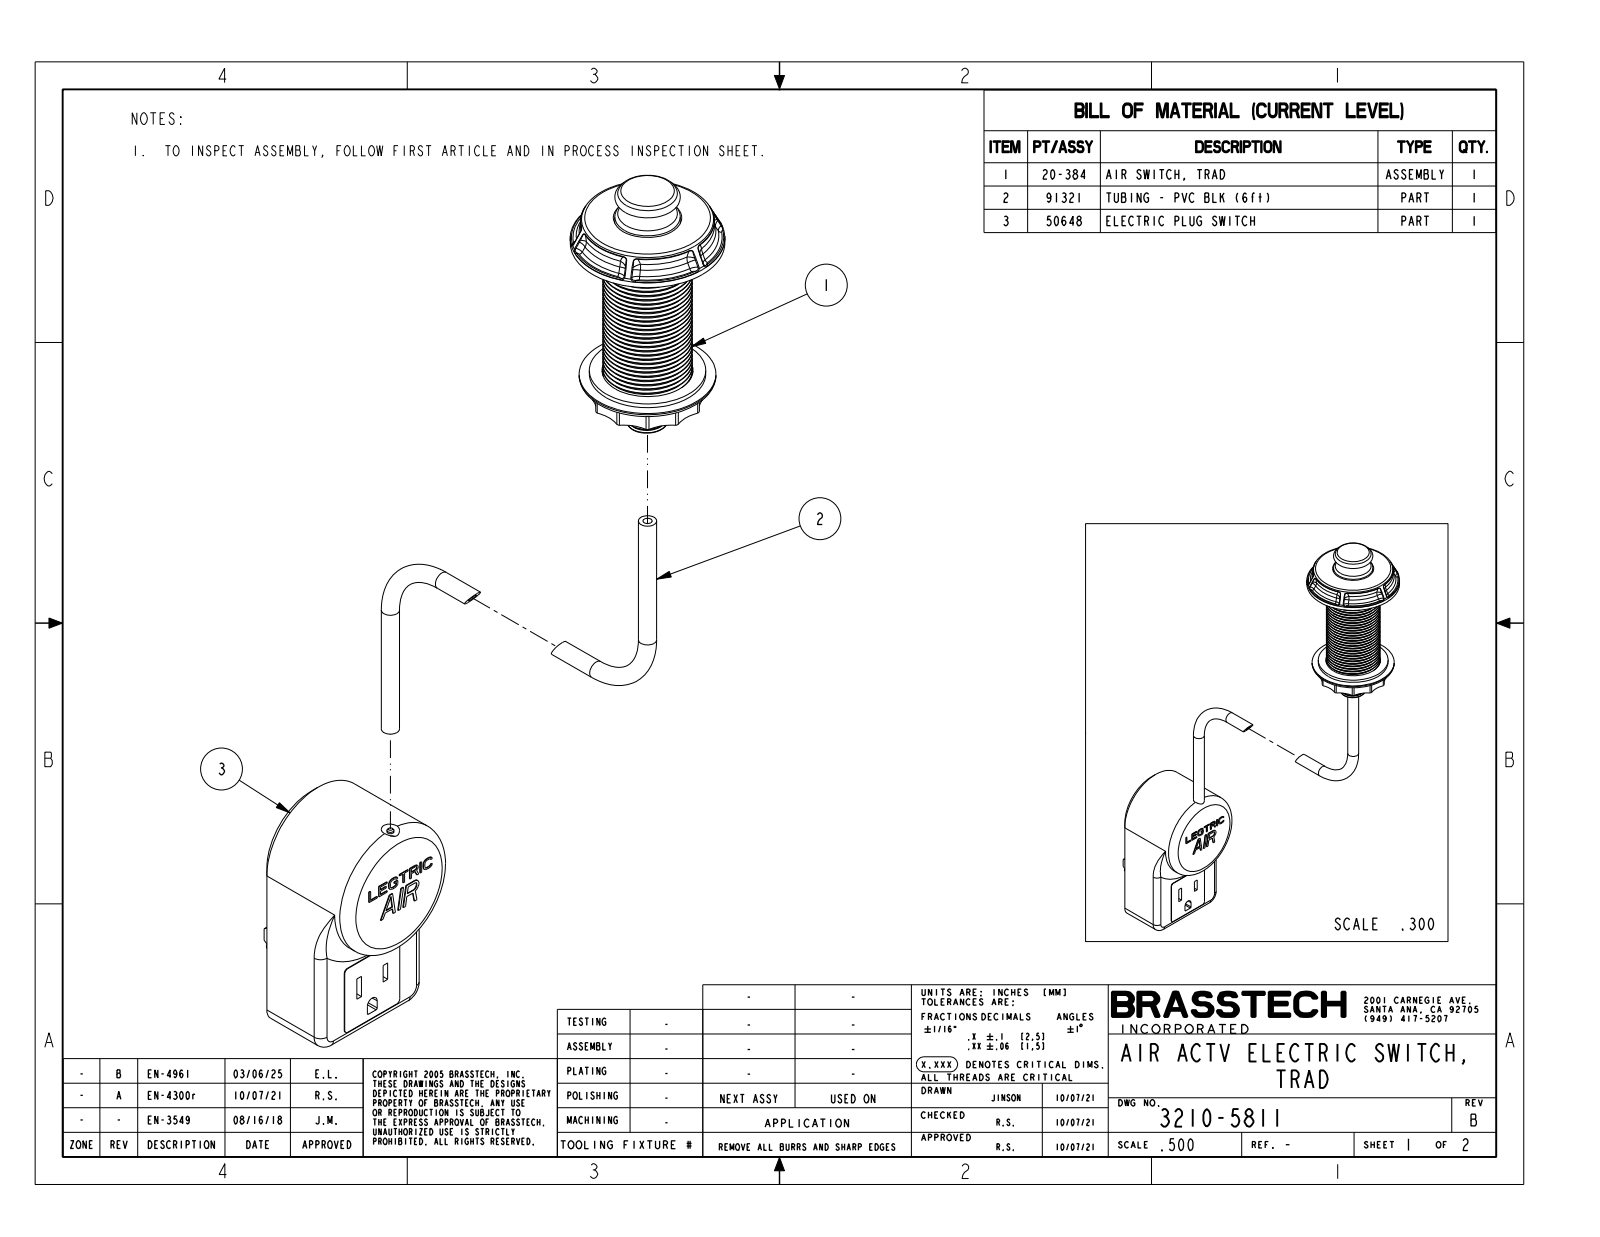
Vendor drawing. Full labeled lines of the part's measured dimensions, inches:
Part name (STEP PRODUCT): 3210-5811
STEP written by: CREO PARAMETRIC BY PTC INC, 2018400 (AUTOMOTIVE_DESIGN)
Units: inches
Bodies: 3 solids, 626 faces (259 planar, 155 cylindrical, 212 other)
Overall size (bounding box): 12.984 × 8.436 × 2.125
Volume: 14.38 in³ · Surface area: 69.7 in²
Round holes (diameter × count): ⌀0.125 ×4, ⌀0.94 ×1, ⌀1.25 ×1
Round bosses / shafts (diameter × count): ⌀0.25 ×3, ⌀2.125 ×1, ⌀1.99 ×1, ⌀1.88 ×1, ⌀1.6 ×1, ⌀1.23 ×1, ⌀1.153 ×1, ⌀1.135 ×1
Partial cylindrical surfaces — rounded edges, fillets, slot ends (radius × count): R0.5 ×12, R0.06 ×4, R0.125 ×3, R0.02 ×2, R0.25 ×2, R0.095 ×1, R0.81 ×1, R0.92 ×1
Main face-to-face distances: 1.99, 1.7, 0.08, 0.425, 0.36, 12.059, 12.484, 0.52, 1.18, 0.44
Hole centre spacings: 5
